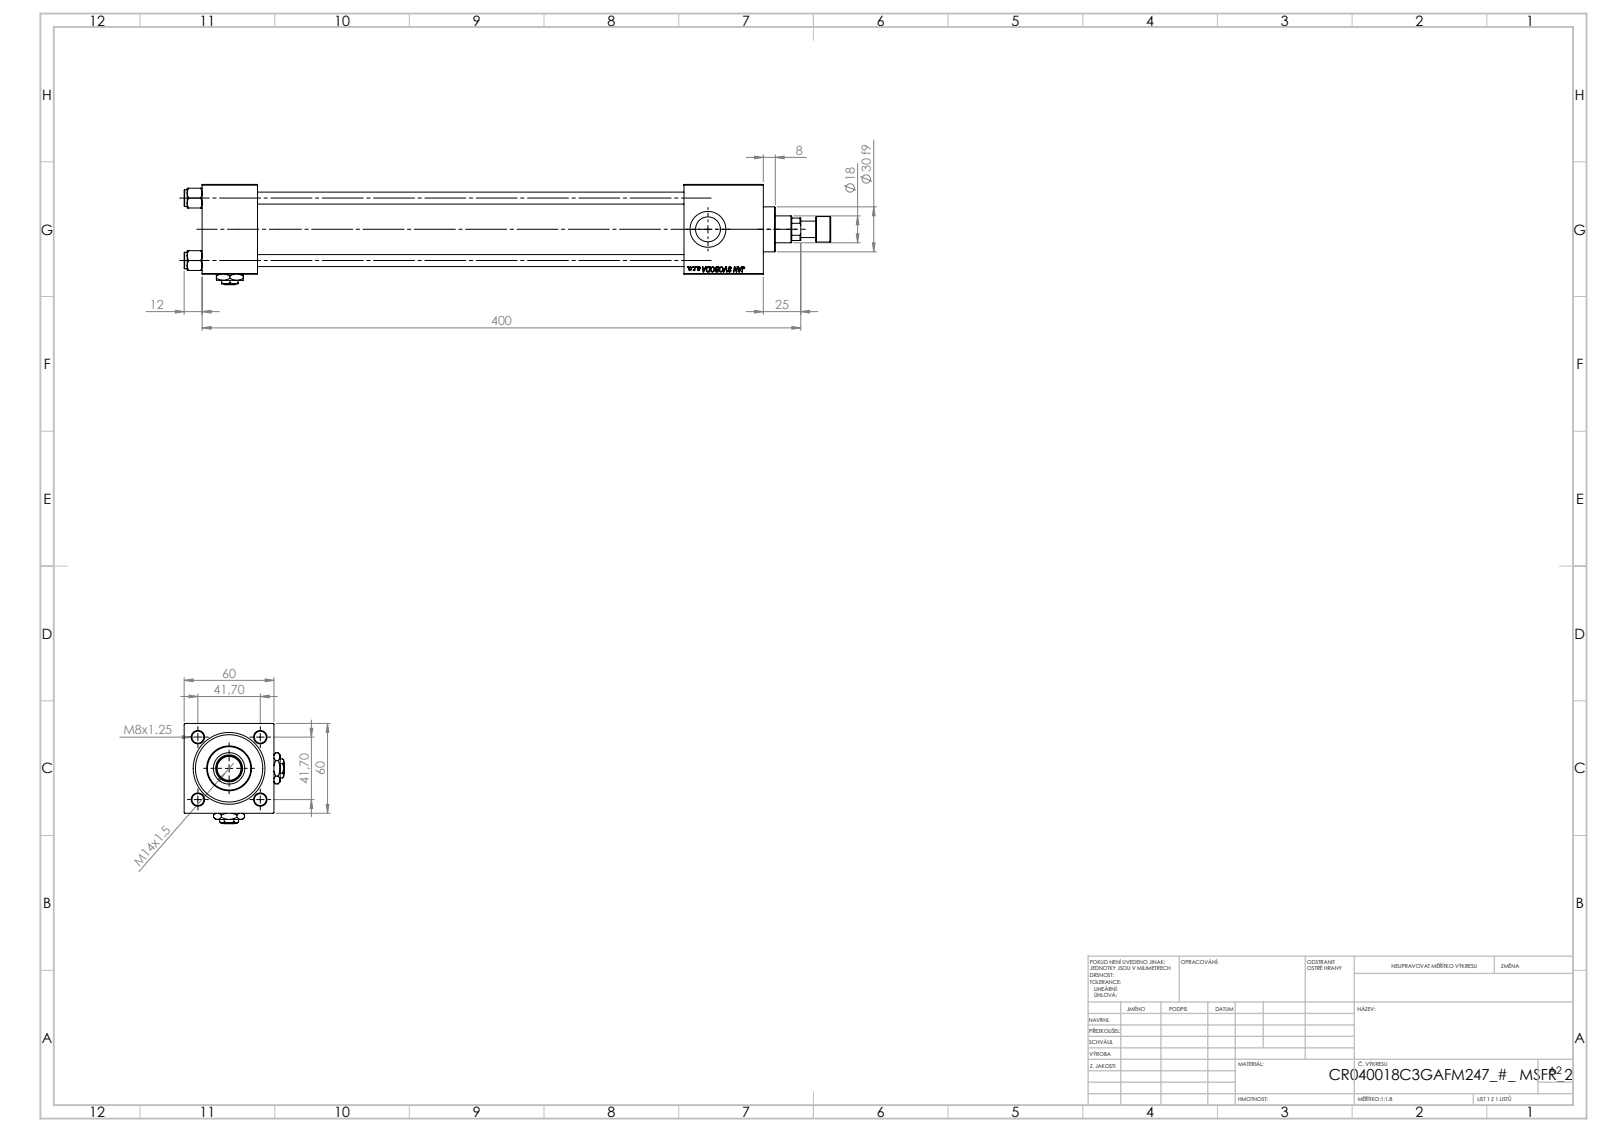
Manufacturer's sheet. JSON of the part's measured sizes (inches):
{"part_name": "V215CR_VCP_C; Zatka_pro_OIL_PORT; V215CR_C_Body; NUT_M5_C (+3 more)", "step_written_by": "SolidWorks 2019 (CONFIG_CONTROL_DESIGN)", "units": "inches", "bodies": {"solids": 14, "faces": 1267, "planar": 579, "cylindrical": 106, "other": 582}, "overall_size": [17.008, 2.638, 2.638], "volume_in3": 36.46, "surface_area_in2": 320.4, "round_holes": [[0.315, 4], [0.098, 2], [0.276, 2], [0.656, 2], [0.945, 2], [0.335, 1], [0.709, 1], [0.827, 1], [1.22, 1], [1.575, 1], [1.772, 1]], "round_bosses_or_shafts": [[0.433, 5], [1.811, 1], [1.181, 1], [0.669, 1]], "face_to_face_distances": [2.362, 1.457, 14.764, 13.307, 2.087, 12.677, 11.22, 13.634, 12.177, 0.957], "hole_center_spacings": [0.821, 1.161, 1.642, 1.832, 0.817, 2.322, 1.634]}
